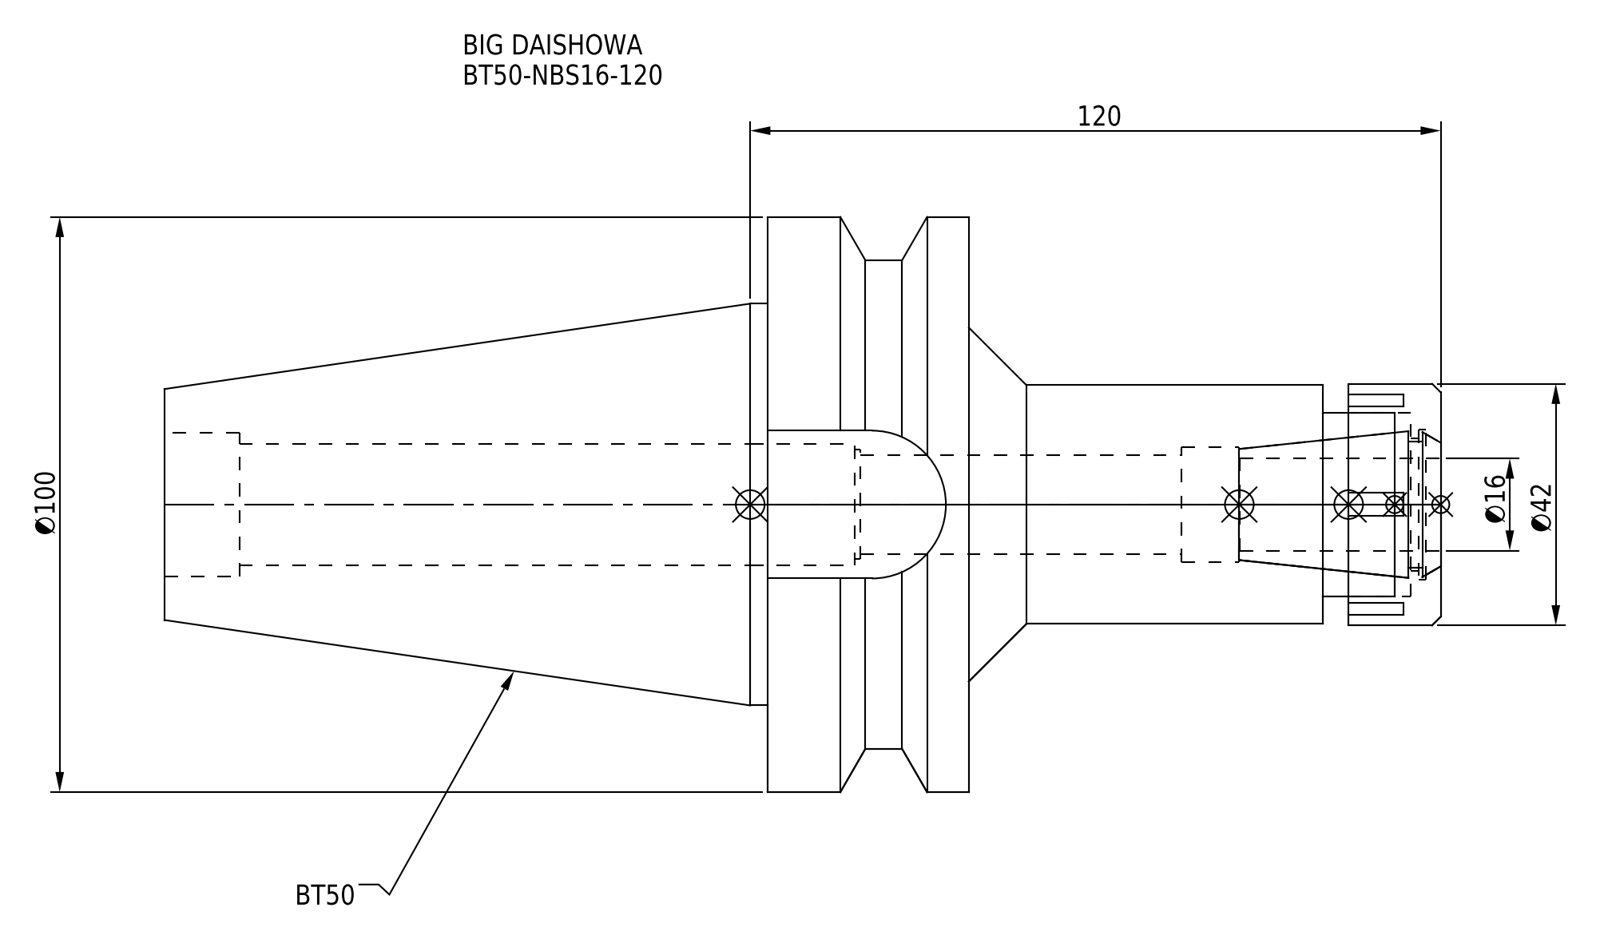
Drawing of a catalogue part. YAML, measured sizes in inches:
part_name: "NBN16_1.stp; BT50NB16120-160_ASM.stp; BT50-NBS16-120; BT50-NBS16-120-FreeParts (+3 more)"
step_written_by: "SolidWorks 2019 (CONFIG_CONTROL_DESIGN)"
units: inches
bodies: {solids: 2, faces: 93, planar: 45, cylindrical: 34, other: 14}
overall_size: [8.732, 3.937, 3.937]
volume: 32.6
surface_area: 112.9
round_holes:
  - {diameter: 0.681, count: 1}
  - {diameter: 0.748, count: 1}
  - {diameter: 0.787, count: 1}
  - {diameter: 0.835, count: 1}
  - {diameter: 0.906, count: 1}
  - {diameter: 0.984, count: 1}
  - {diameter: 1.024, count: 1}
  - {diameter: 1.26, count: 1}
round_bosses_or_shafts:
  - {diameter: 3.937, count: 1}
  - {diameter: 3.346, count: 1}
  - {diameter: 2.75, count: 1}
  - {diameter: 1.654, count: 1}
  - {diameter: 1.634, count: 1}
partial_cylinders:
  - {radius: 0.506, count: 1}
face_to_face_distances: [1.378, 3.228, 4.606, 8.732, 5.504, 4.126, 2.787, 0.315, 0.807, 2.421]
